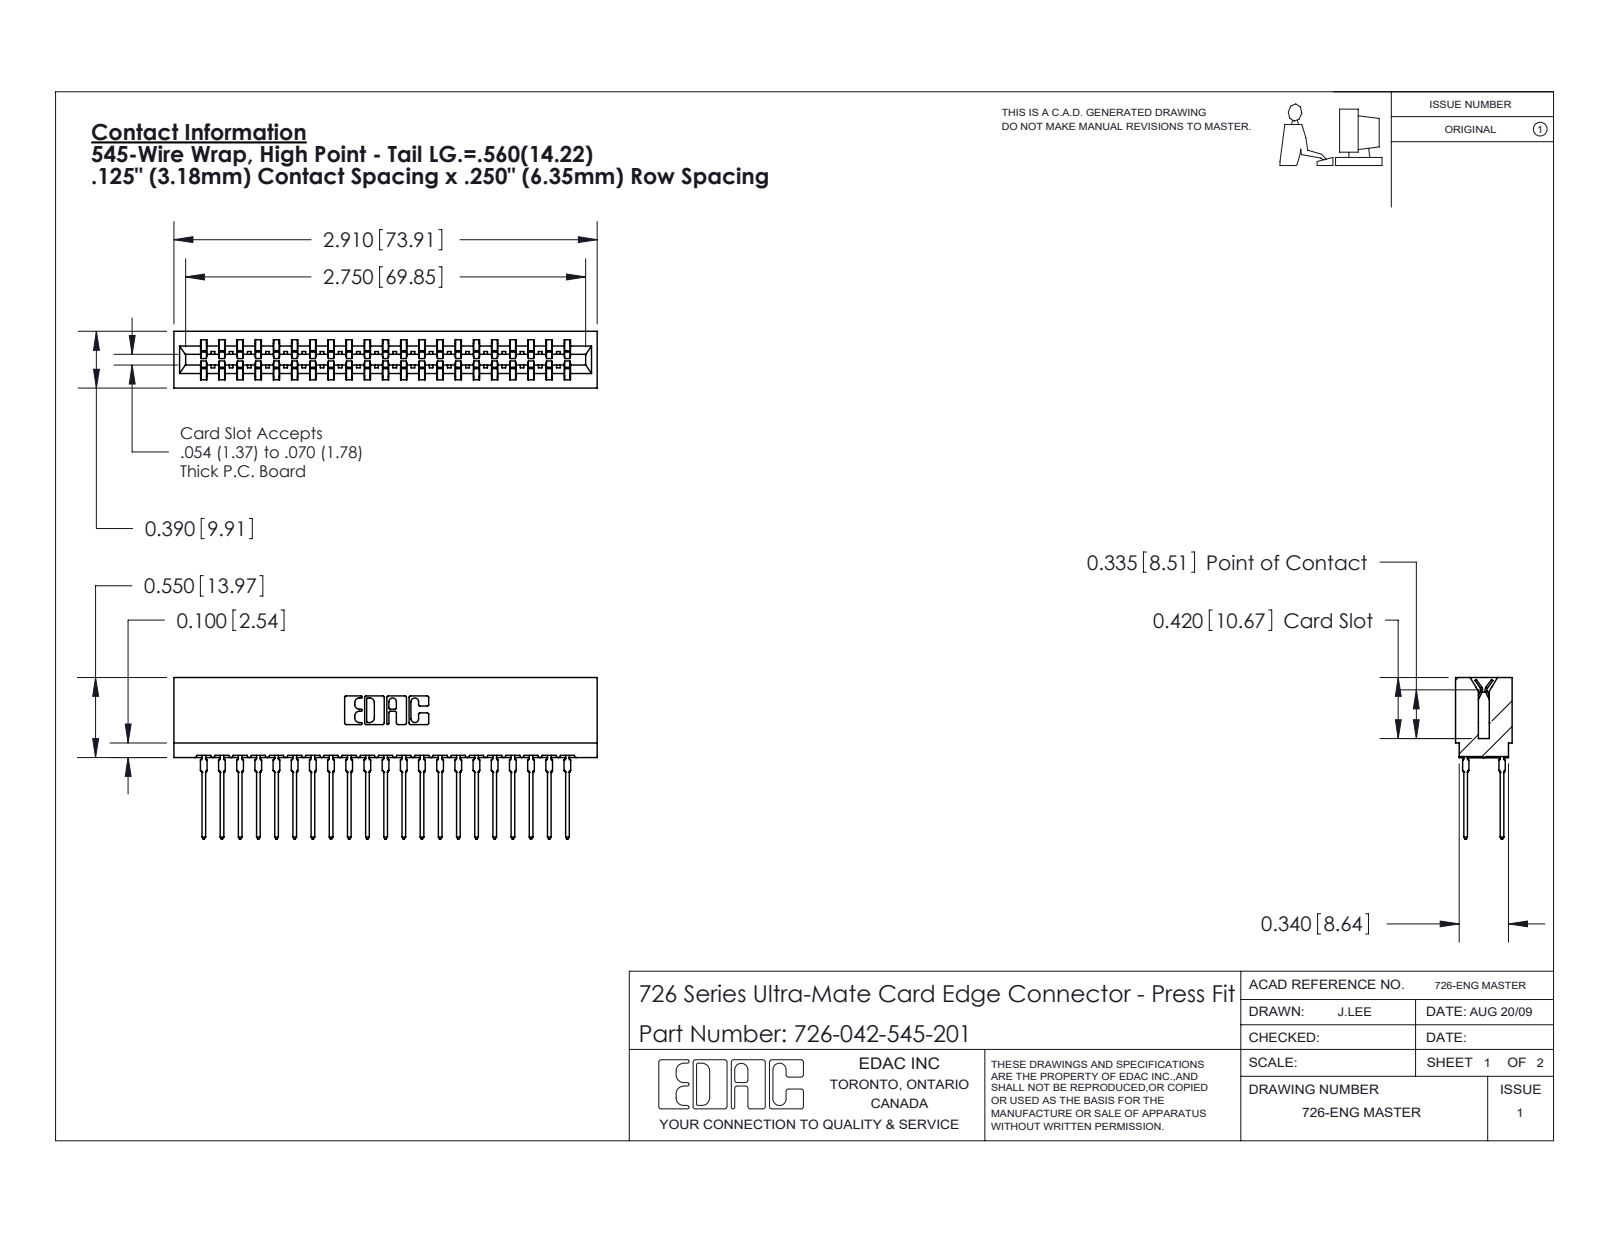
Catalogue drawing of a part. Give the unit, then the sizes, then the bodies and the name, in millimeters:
Units: millimetres
Overall size (bounding box): 73.9 × 28.2 × 9.9
Partial cylindrical surfaces — rounded edges, fillets, slot ends (radius × count): R0.5 ×84, R0.3 ×22, R0.4 ×22, R0.1 ×8, R0.3 ×8, R0.2 ×6, R0.8 ×6, R0.7 ×3
Main face-to-face distances: 1.4, 8.5, 6.4, 0.6, 7.8, 9.9, 2.1, 7, 12.7, 19.1
Volume: 7 060 mm³ · Surface area: 12 060 mm²
Bodies: 43 solids, 3856 faces (1987 planar, 777 cylindrical, 1092 other)
Part name (STEP PRODUCT): 726 Part_.515 Slot Depth - 01; 726-042-545-201; 746-292-001_545
STEP written by: SolidWorks 2020 (CONFIG_CONTROL_DESIGN)
